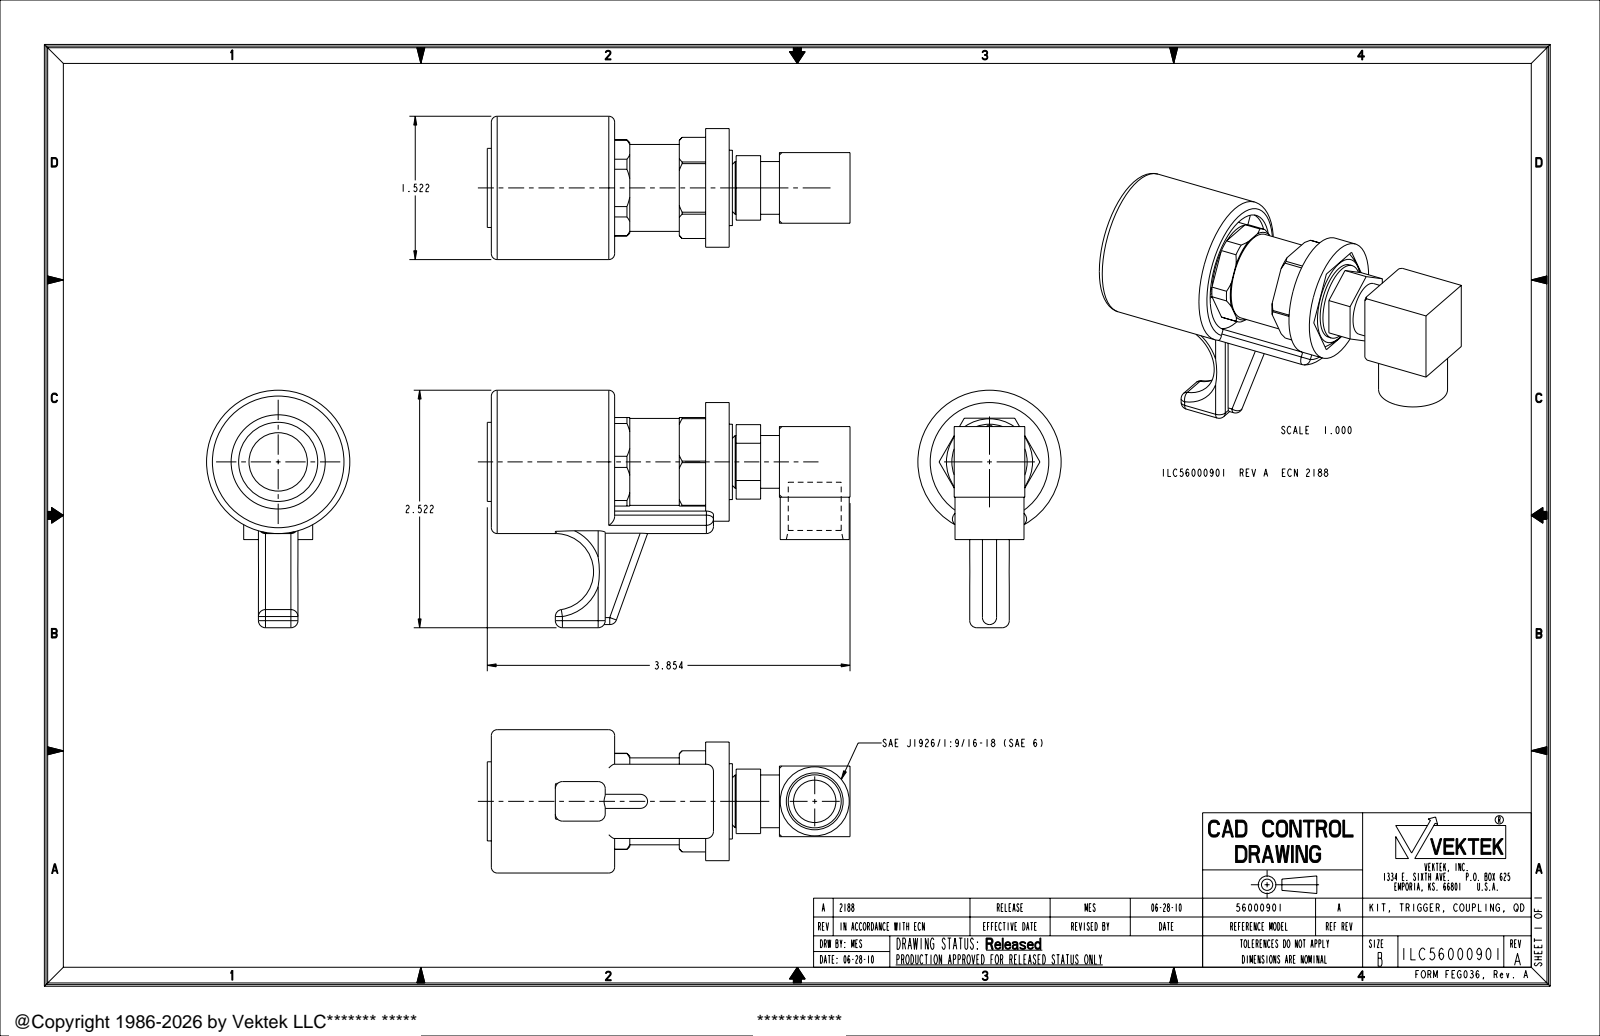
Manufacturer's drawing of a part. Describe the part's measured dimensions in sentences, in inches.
The part is named "ILC56000901". Its 3-D file was written by "PRO/ENGINEER BY PARAMETRIC TECHNOLOGY CORPORATION, 2007460 (AUTOMOTIVE_DESIGN_CC2)". It is 1 solid with 198 faces: 89 planar, 64 cylindrical and 45 other. Overall it measures 3.854 by 2.522 by 1.522 inches. Its volume is 3.718 cubic inches and its surface area 35.37 square inches. Round holes: 1 of diameter 0.094, 1 of diameter 0.3, 1 of diameter 0.45, 1 of diameter 0.509, 1 of diameter 0.563, 1 of diameter 0.62, 1 of diameter 1.26. Round bosses or shafts: 1 of diameter 1.522, 1 of diameter 1.195, 1 of diameter 0.923, 1 of diameter 0.84, 1 of diameter 0.8, 1 of diameter 0.733, 1 of diameter 0.56. Partial cylindrical surfaces (rounded edges, fillets, slot ends): 14 of radius 0.075, 2 of radius 0.074, 1 of radius 0.01, 1 of radius 0.059, 1 of radius 0.406, 1 of radius 0.507, 1 of radius 0.511, 1 of radius 0.537. The main face-to-face distances are 0.75, 2.527, 3.811, 1.284, 0.3, 2.277, 0.25, 1.534, 0.5, 0.135.
